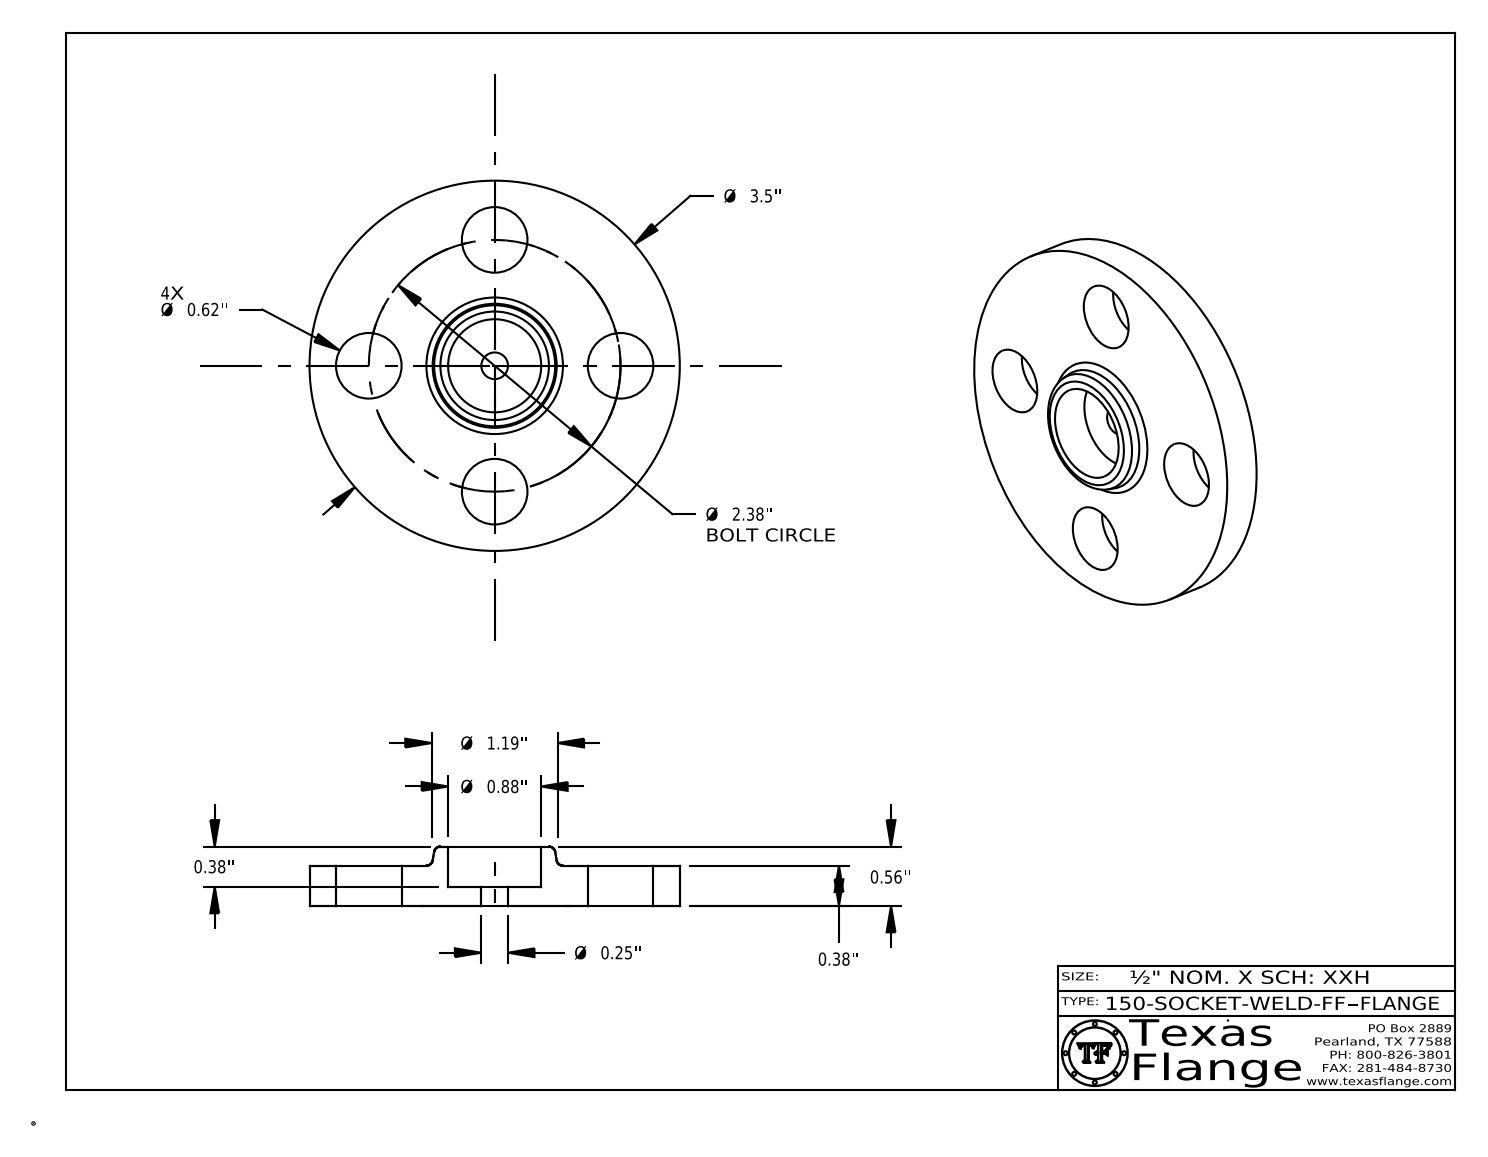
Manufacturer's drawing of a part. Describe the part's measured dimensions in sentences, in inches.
The part is named "150-SOCKET-WELD-FF". Its 3-D file was written by "CATIA V5 STEP AP214 (AUTOMOTIVE_DESIGN)". It is 1 solid with 410 faces: 370 planar, 34 cylindrical and 6 other. Overall it measures 3.5 by 3.5 by 0.56 inches. Its volume is 3.146 cubic inches and its surface area 25.58 square inches. Round holes: 4 of diameter 0.62, 1 of diameter 0.252, 1 of diameter 0.495, 1 of diameter 0.88. Round bosses or shafts: 8 of diameter 0.03, 1 of diameter 3.5, 1 of diameter 0.39. The main face-to-face distances are 0.38, 0.18, 0.2, 0.56, 0.365, 0.185, 0.015, 0.195, 0.148, 0.145. The hole center spacings are 1.19, 1.683, 0.911, 2.199, 2.38, 1.19.
